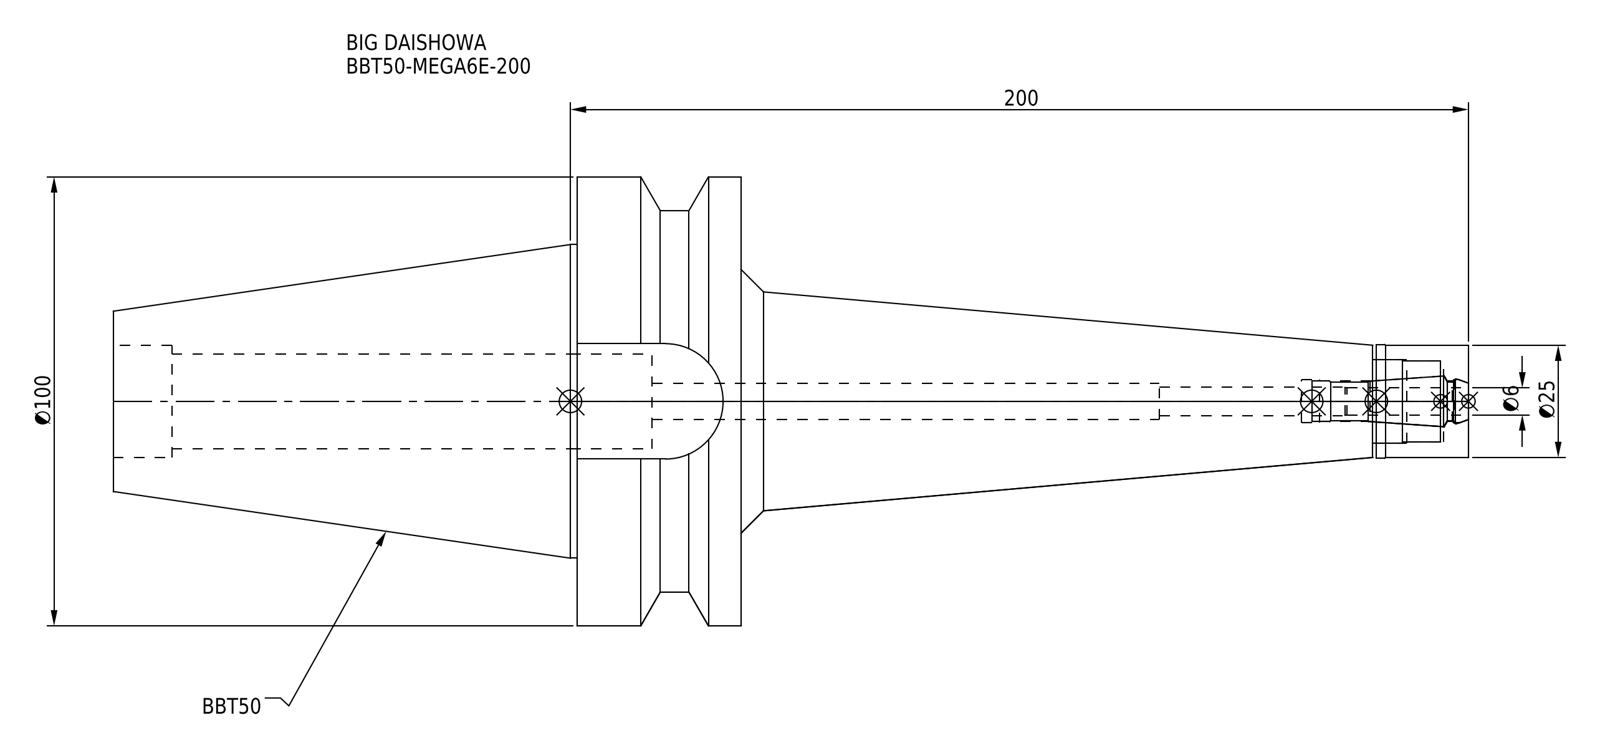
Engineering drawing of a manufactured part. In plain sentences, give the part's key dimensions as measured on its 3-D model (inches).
The part is named "BBT50-MEGA6E-200-060.stp; BBT50-MEGA6E-200; BBT50ME06200-060_ASM.stp; BBT50-MEGA6E-200-060-FreeParts (+3 more)". Its 3-D file was written by "SolidWorks 2019 (CONFIG_CONTROL_DESIGN)". It is 2 solids with 81 faces: 21 planar, 40 cylindrical and 20 other. Overall it measures 11.882 by 3.937 by 3.937 inches. Its volume is 37.64 cubic inches and its surface area 119.3 square inches. Round holes: 1 of diameter 0.252, 1 of diameter 0.315, 1 of diameter 0.354, 1 of diameter 0.378, 1 of diameter 0.39, 1 of diameter 0.709, 1 of diameter 0.728, 1 of diameter 0.835, 1 of diameter 0.984. Round bosses or shafts: 1 of diameter 3.937, 1 of diameter 3.346, 1 of diameter 2.75, 1 of diameter 0.996. Partial cylindrical surfaces (rounded edges, fillets, slot ends): 1 of radius 0.506. The main face-to-face distances are 1.437, 5.504, 4.067, 2.787, 1.012, 6.378, 7.815, 11.882, 0.657, 7.157.
